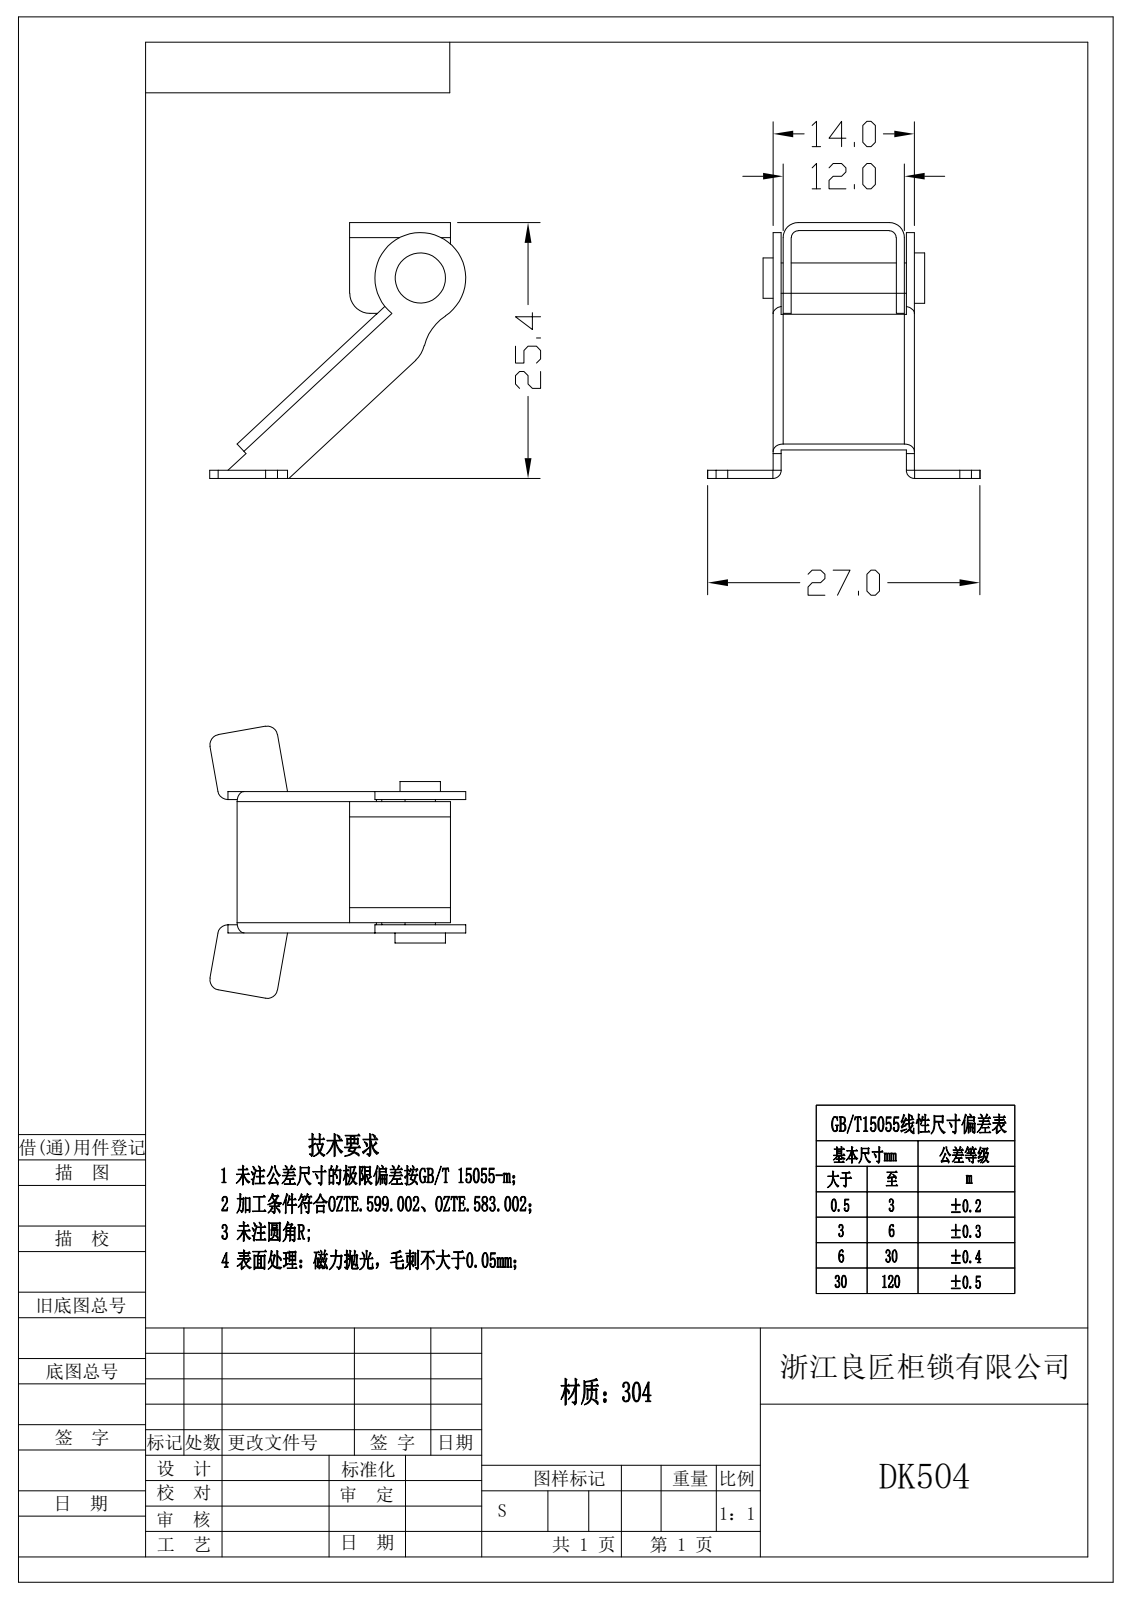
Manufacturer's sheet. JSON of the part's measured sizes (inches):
{"step_written_by": "Rhino 8.5 (CONFIG_CONTROL_DESIGN)", "units": "inches", "bodies": {"solids": 2, "faces": 128, "planar": 64, "cylindrical": 44, "other": 20}, "overall_size": [1.061, 1.006, 0.998], "volume_in3": 0.057, "surface_area_in2": 3.581, "round_holes": [[0.118, 1], [0.157, 1], [0.196, 1]], "partial_cylinders_radius": [[0.004, 4], [0.039, 4], [0.02, 3], [0.031, 3], [0.028, 2], [0.059, 2], [0.079, 2], [0.008, 1]], "face_to_face_distances": [0.039, 0.512, 0.472, 0.031, 0.551, 0.071, 0.48, 0.441, 0.059, 0.939]}
